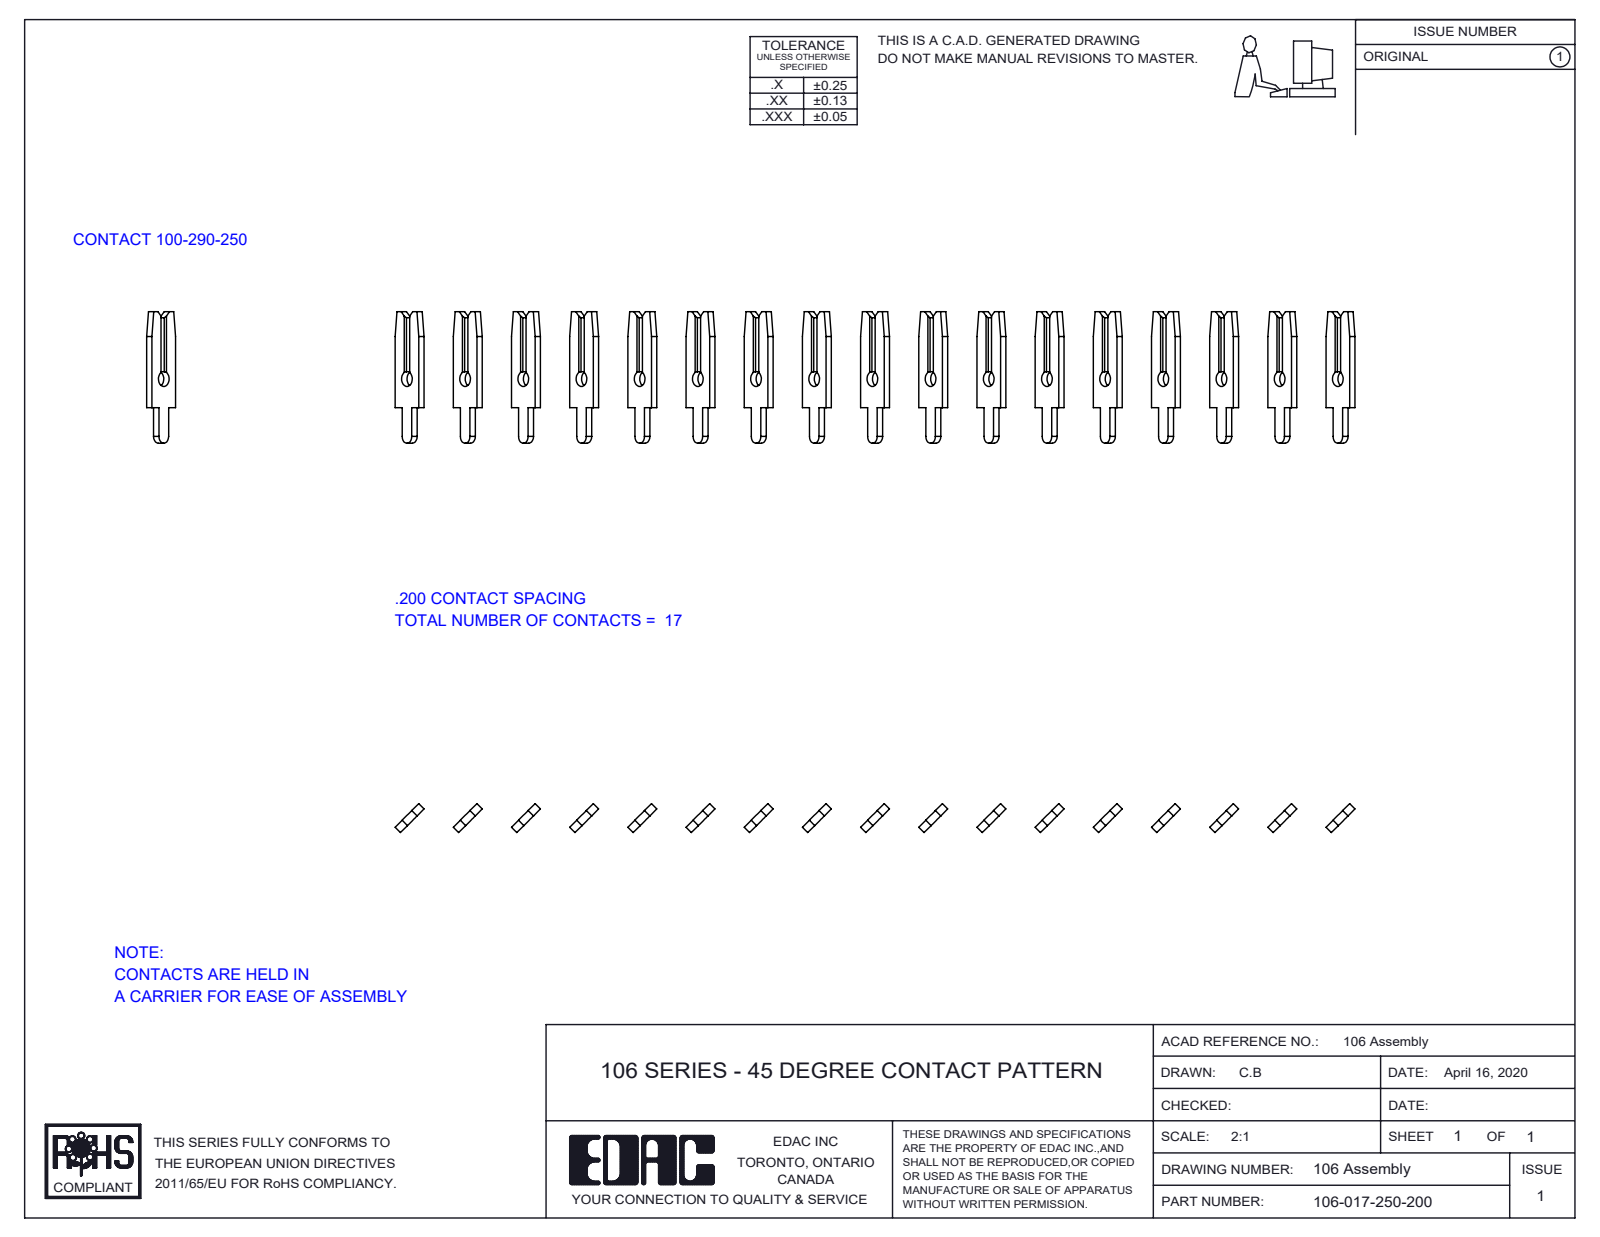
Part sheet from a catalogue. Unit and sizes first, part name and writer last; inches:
Units: inches
Overall size (bounding box): 3.3 × 0.452 × 0.1
Round holes (diameter × count): ⌀0.052 ×17
Partial cylindrical surfaces — rounded edges, fillets, slot ends (radius × count): R0.024 ×17
Main face-to-face distances: 0.141, 0.283, 0.848, 0.707, 0.99, 0.566, 0.424, 1.131, 0.424, 1.272
Hole centre spacings: 0.141, 0.283, 0.424, 0.848, 0.99, 0.566, 0.707, 1.131
Volume: 0.016 in³ · Surface area: 1.933 in²
Bodies: 17 solids, 408 faces (340 planar, 68 cylindrical, 0 other)
Part name (STEP PRODUCT): 100-290-001_100-290-250; 106-017-250-200
STEP written by: SolidWorks 2016 (CONFIG_CONTROL_DESIGN)
